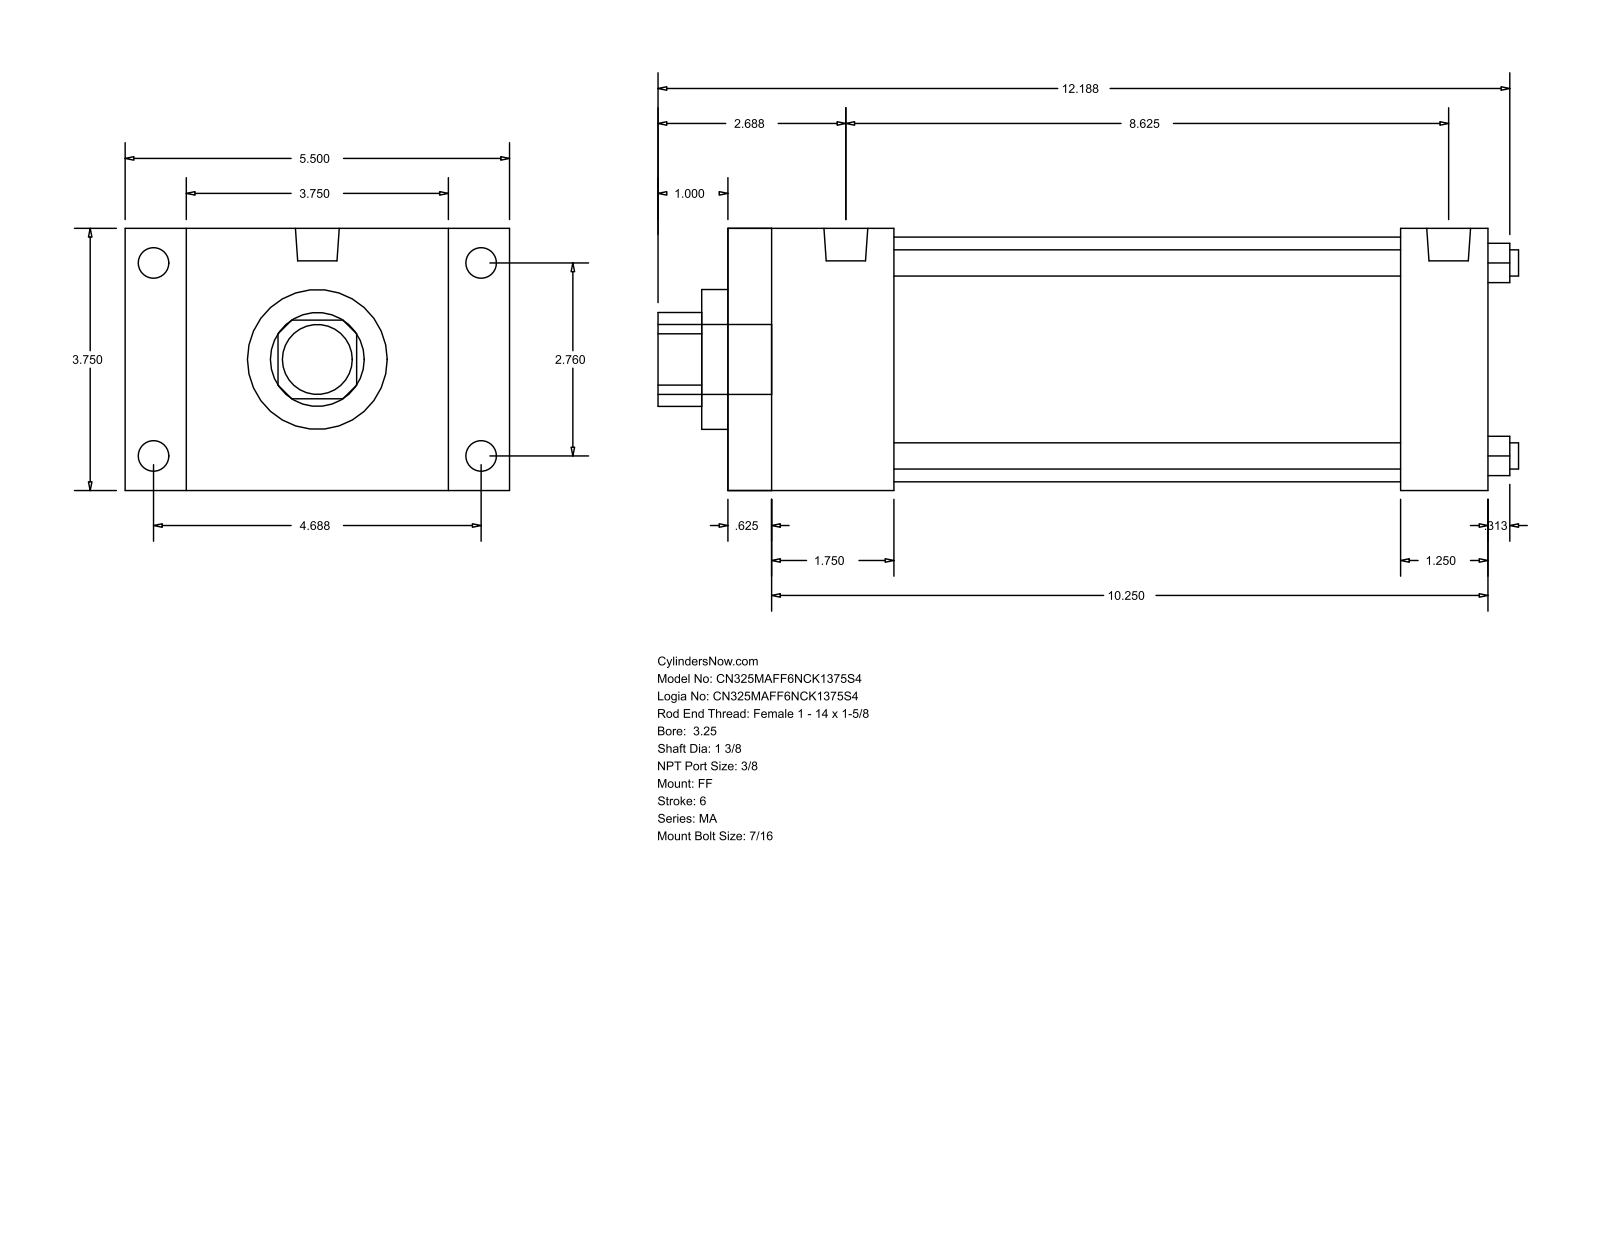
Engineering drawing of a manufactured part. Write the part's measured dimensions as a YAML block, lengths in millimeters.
part_name: "MA_FF__0325_1.375"
step_written_by: "GSSL Pune (CONFIG_CONTROL_DESIGN)"
units: millimeters
bodies: {solids: 0, faces: 92, planar: 64, cylindrical: 28, other: 0}
overall_size: [312.74, 139.7, 95.25]
round_holes:
  - {diameter: 9.53, count: 4}
  - {diameter: 34.92, count: 1}
  - {diameter: 50.8, count: 1}
  - {diameter: 88.9, count: 1}
round_bosses_or_shafts:
  - {diameter: 11.11, count: 8}
  - {diameter: 15.93, count: 2}
  - {diameter: 25.4, count: 1}
partial_cylinders:
  - {radius: 17.06, count: 1}
face_to_face_distances: [95.24, 276.22, 15.87, 260.35, 22.23, 117.47, 60.32, 244.48, 44.45, 228.61]
hole_center_spacings: [49.57, 70.1, 99.14]
